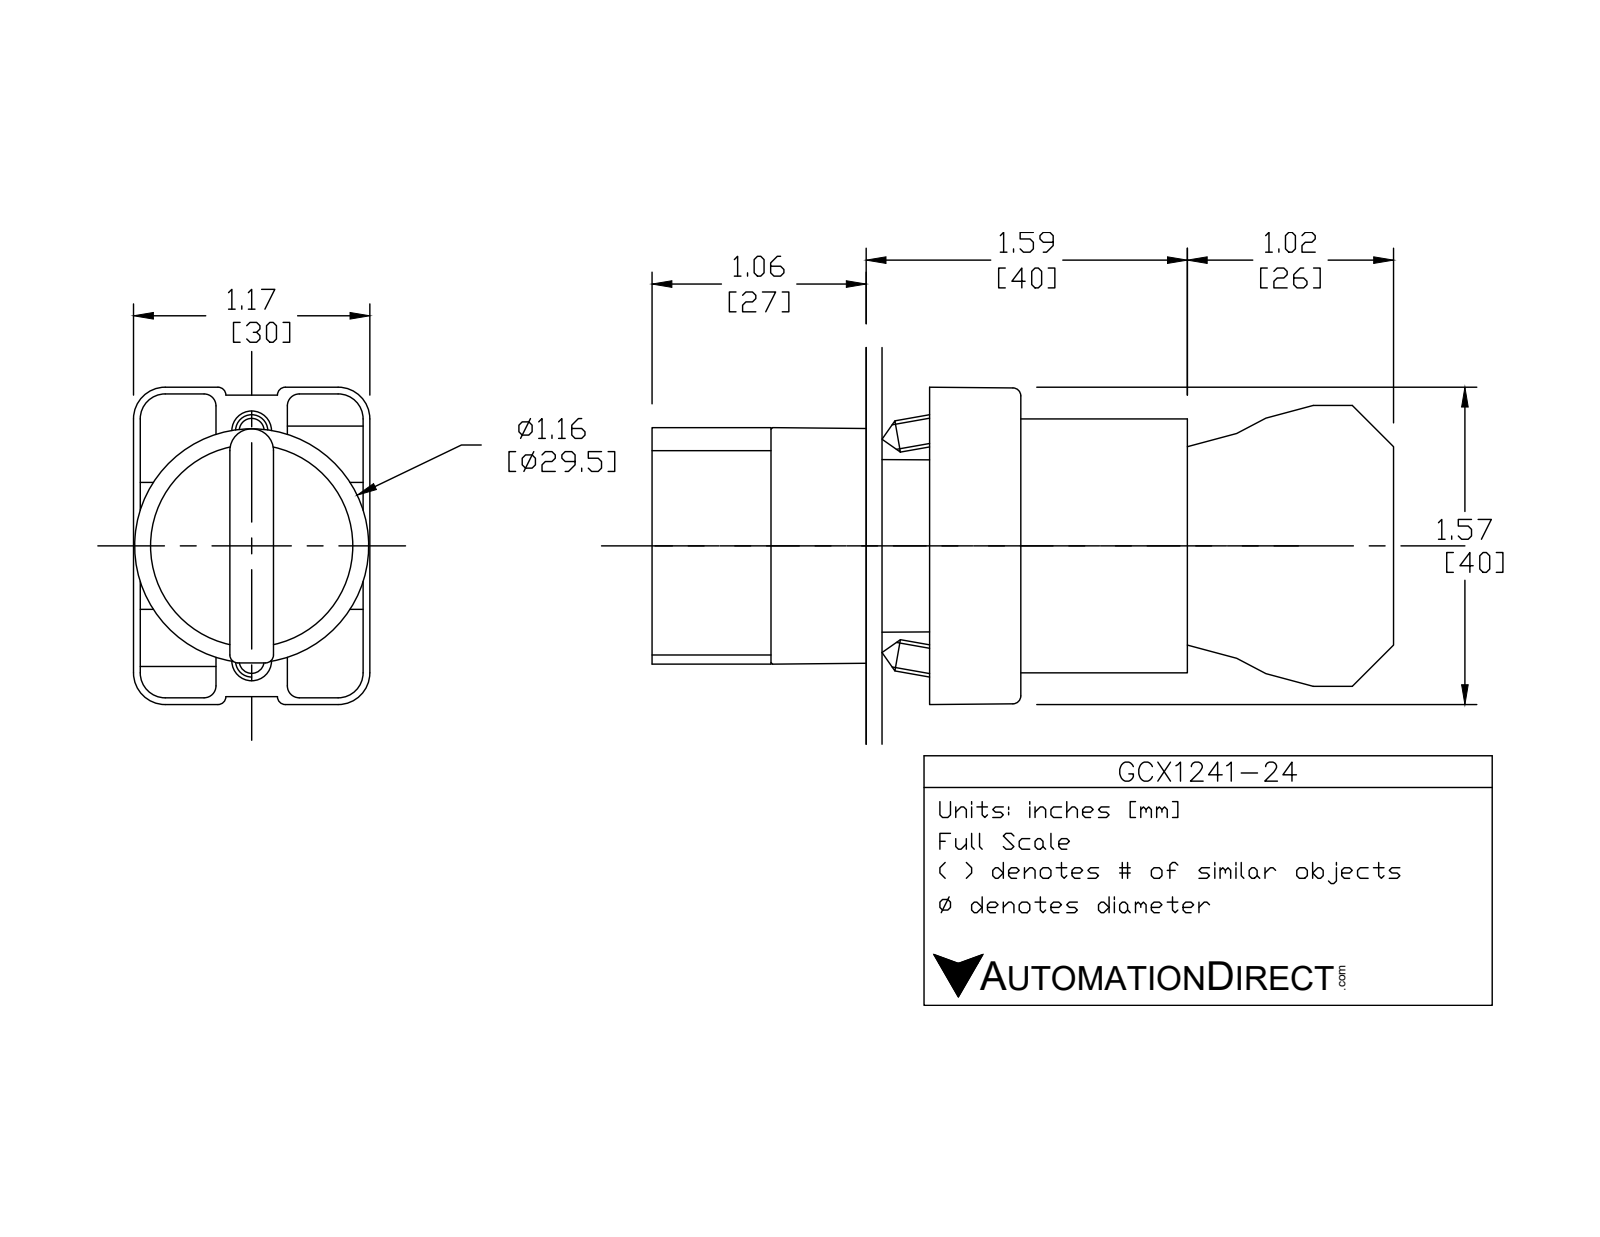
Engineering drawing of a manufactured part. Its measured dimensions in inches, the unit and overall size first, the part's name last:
Units: inches
Overall size (bounding box): 3.653 × 1.581 × 1.177
Round holes (diameter × count): ⌀0.079 ×2, ⌀0.124 ×2, ⌀0.13 ×2, ⌀0.087 ×1, ⌀0.197 ×1, ⌀0.469 ×1, ⌀0.878 ×1, ⌀0.888 ×1, ⌀1.024 ×1
Round bosses / shafts (diameter × count): ⌀0.157 ×4, ⌀1.175 ×1, ⌀1.004 ×1, ⌀0.945 ×1, ⌀0.856 ×1, ⌀0.78 ×1, ⌀0.504 ×1
Partial cylindrical surfaces — rounded edges, fillets, slot ends (radius × count): R0.059 ×24, R0.041 ×12, R0.124 ×12, R0.157 ×12, R0.039 ×9, R0.128 ×2, R0.02 ×1, R0.063 ×1
Main face-to-face distances: 0.827, 2.02, 1.193, 0.579, 1.244, 1.171, 0.472, 0.469, 0.031, 0.033
Hole centre spacings: 0.236, 0.544, 0.472, 0.49
Volume: 2.799 in³ · Surface area: 39 in²
Bodies: 8 solids, 445 faces (263 planar, 151 cylindrical, 31 other)
Part name (STEP PRODUCT): ecx1040; ecx1029; GCX1241 OPERATOR; GCX1241-24 (+1 more)
STEP written by: SolidWorks 2016 (AUTOMOTIVE_DESIGN)
